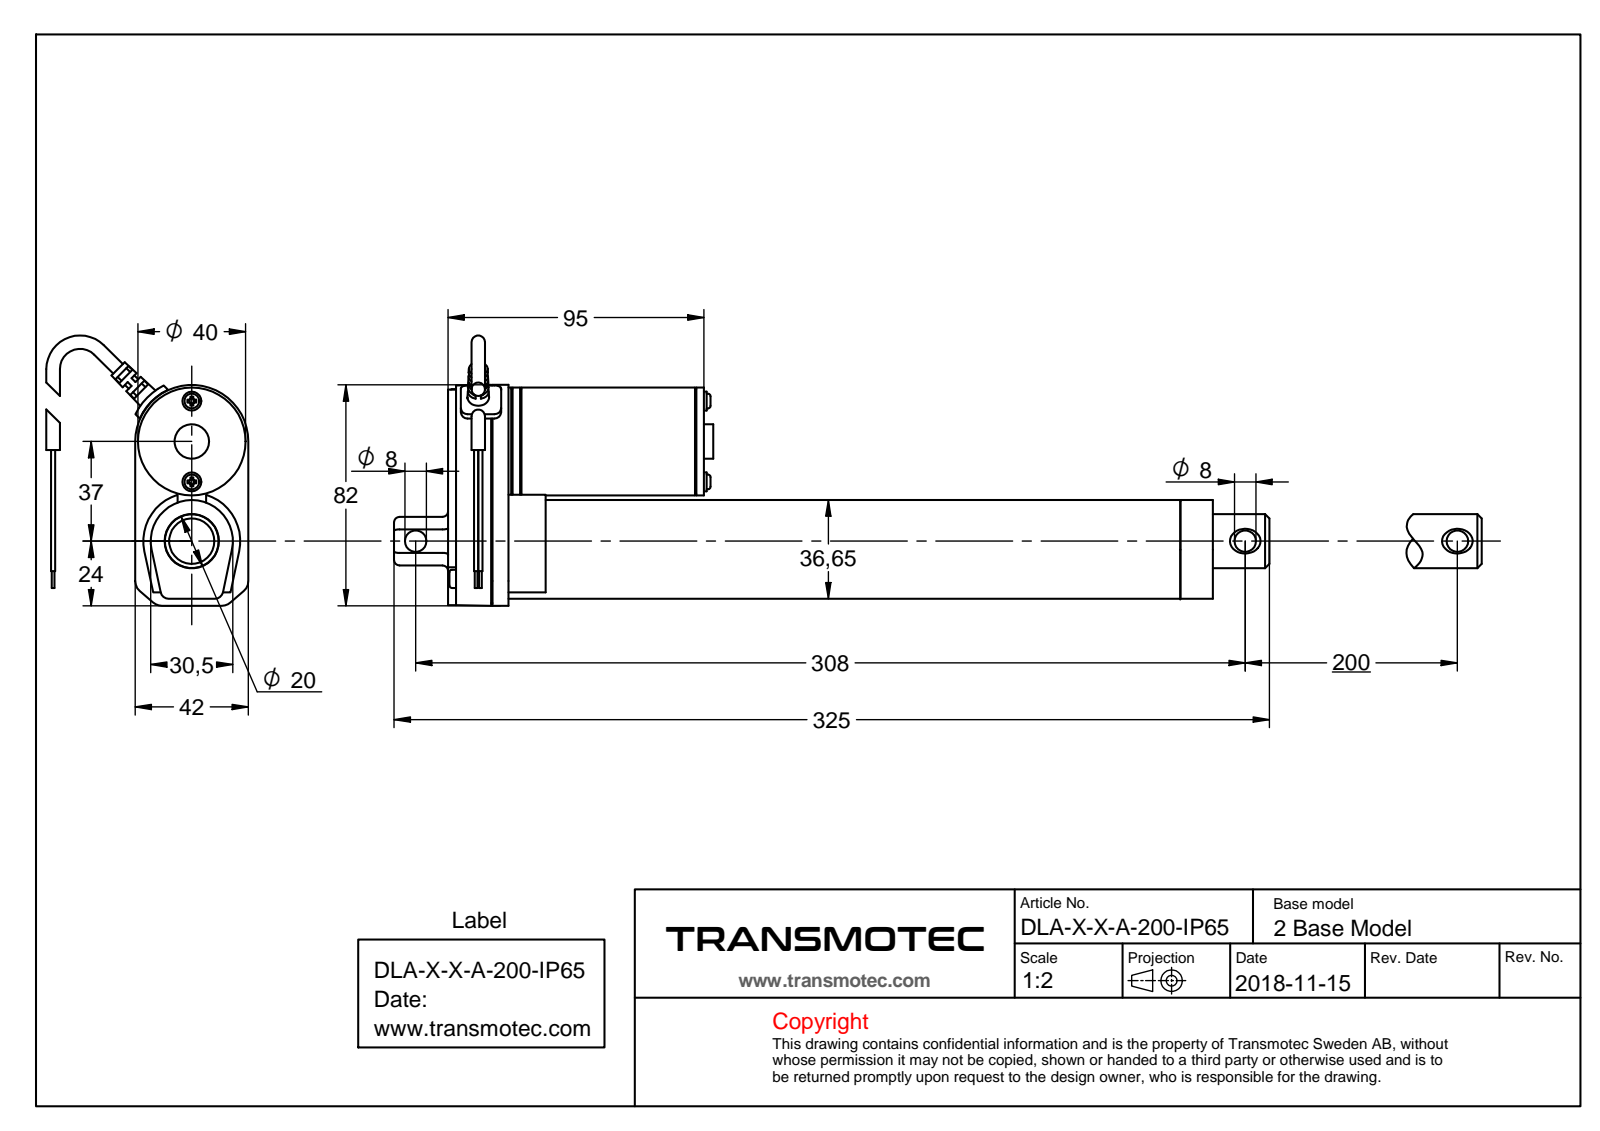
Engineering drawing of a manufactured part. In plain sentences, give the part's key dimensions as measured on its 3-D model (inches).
The part is named "DLA-X-X-A-200-IP65". Its 3-D file was written by "Solid Edge (AUTOMOTIVE_DESIGN)". It is 7 solids with 333 faces: 175 planar, 126 cylindrical and 32 other. Overall it measures 12.913 by 4.324 by 3.131 inches. Its volume is 11.98 cubic inches and its surface area 164.5 square inches. Round holes: 3 of diameter 0.169, 2 of diameter 0.315, 1 of diameter 0.197, 1 of diameter 0.551, 1 of diameter 0.646, 1 of diameter 0.795, 1 of diameter 0.866, 1 of diameter 1.496. Round bosses or shafts: 1 of diameter 1.575, 1 of diameter 0.787, 1 of diameter 0.512, 1 of diameter 0.315, 1 of diameter 0.197, 1 of diameter 0.157, 1 of diameter 0.126. Partial cylindrical surfaces (rounded edges, fillets, slot ends): 12 of radius 0.118, 8 of radius 0.02, 8 of radius 0.079, 4 of radius 0.059, 4 of radius 0.165, 4 of radius 0.197, 3 of radius 0.156, 3 of radius 0.163. The main face-to-face distances are 0.071, 0.071, 0.07, 0.118, 0.098, 0.059, 0.787, 0.669, 0.157, 0.886. The hole center spacings are 0.837, 2.104, 2.712, 0.63, 1.26, 1.457, 2.087, 12.244.
